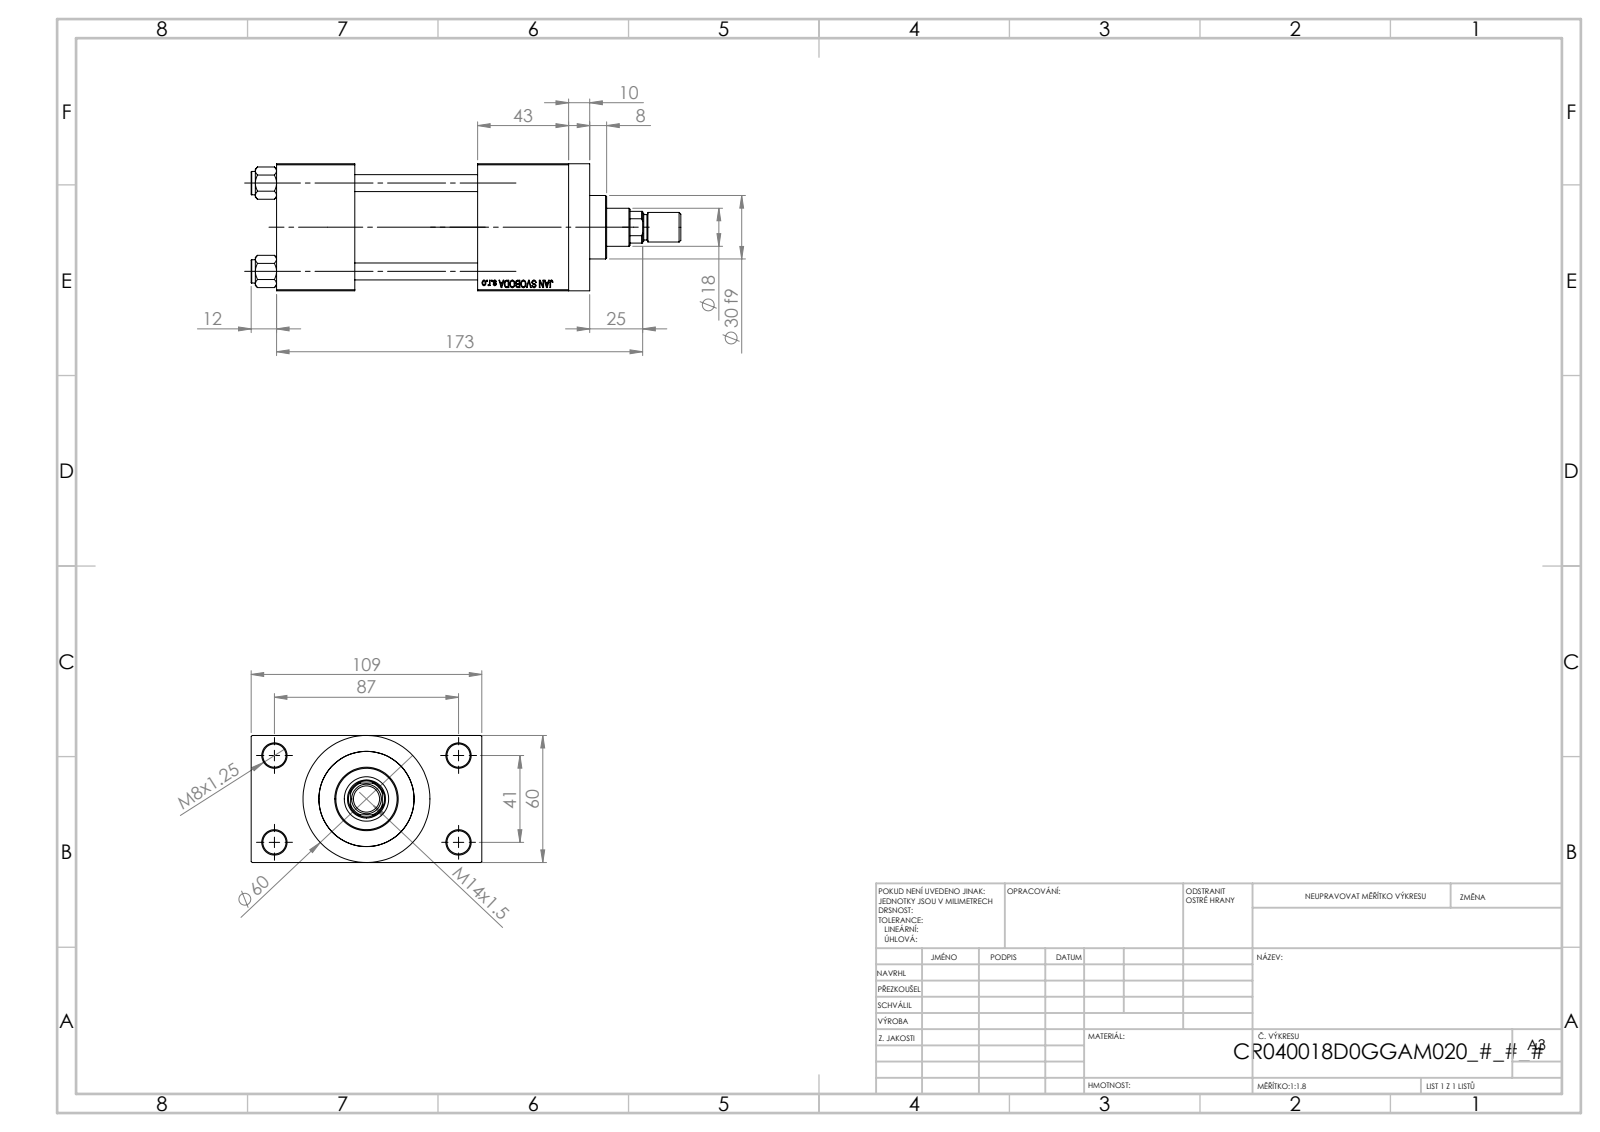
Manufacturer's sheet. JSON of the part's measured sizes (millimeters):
{"part_name": "V215CR_VCP_D; NUT_M5_D; V215CR_D_TYCINKA; V215CR_D_Body (+2 more)", "step_written_by": "SolidWorks 2019 (CONFIG_CONTROL_DESIGN)", "units": "millimeters", "bodies": {"solids": 12, "faces": 1119, "planar": 502, "cylindrical": 93, "other": 524}, "overall_size": [203, 109, 60], "volume_mm3": 520438, "surface_area_mm2": 122393, "round_holes": [[8, 4], [11, 4], [7, 2], [16.66, 2], [24, 2], [8.5, 1], [18, 1], [21, 1], [31, 1], [40, 1], [45, 1]], "round_bosses_or_shafts": [[11, 4], [60, 1], [46, 1], [30, 1], [14, 1], [12, 1]], "partial_cylinders_radius": [[8.5, 1]], "face_to_face_distances": [60, 24.5, 84.5, 58, 37, 95, 43, 138, 101, 109], "hole_center_spacings": [22.65, 29.49, 41.7, 47.15, 48.09, 64.35, 76.49, 41]}
